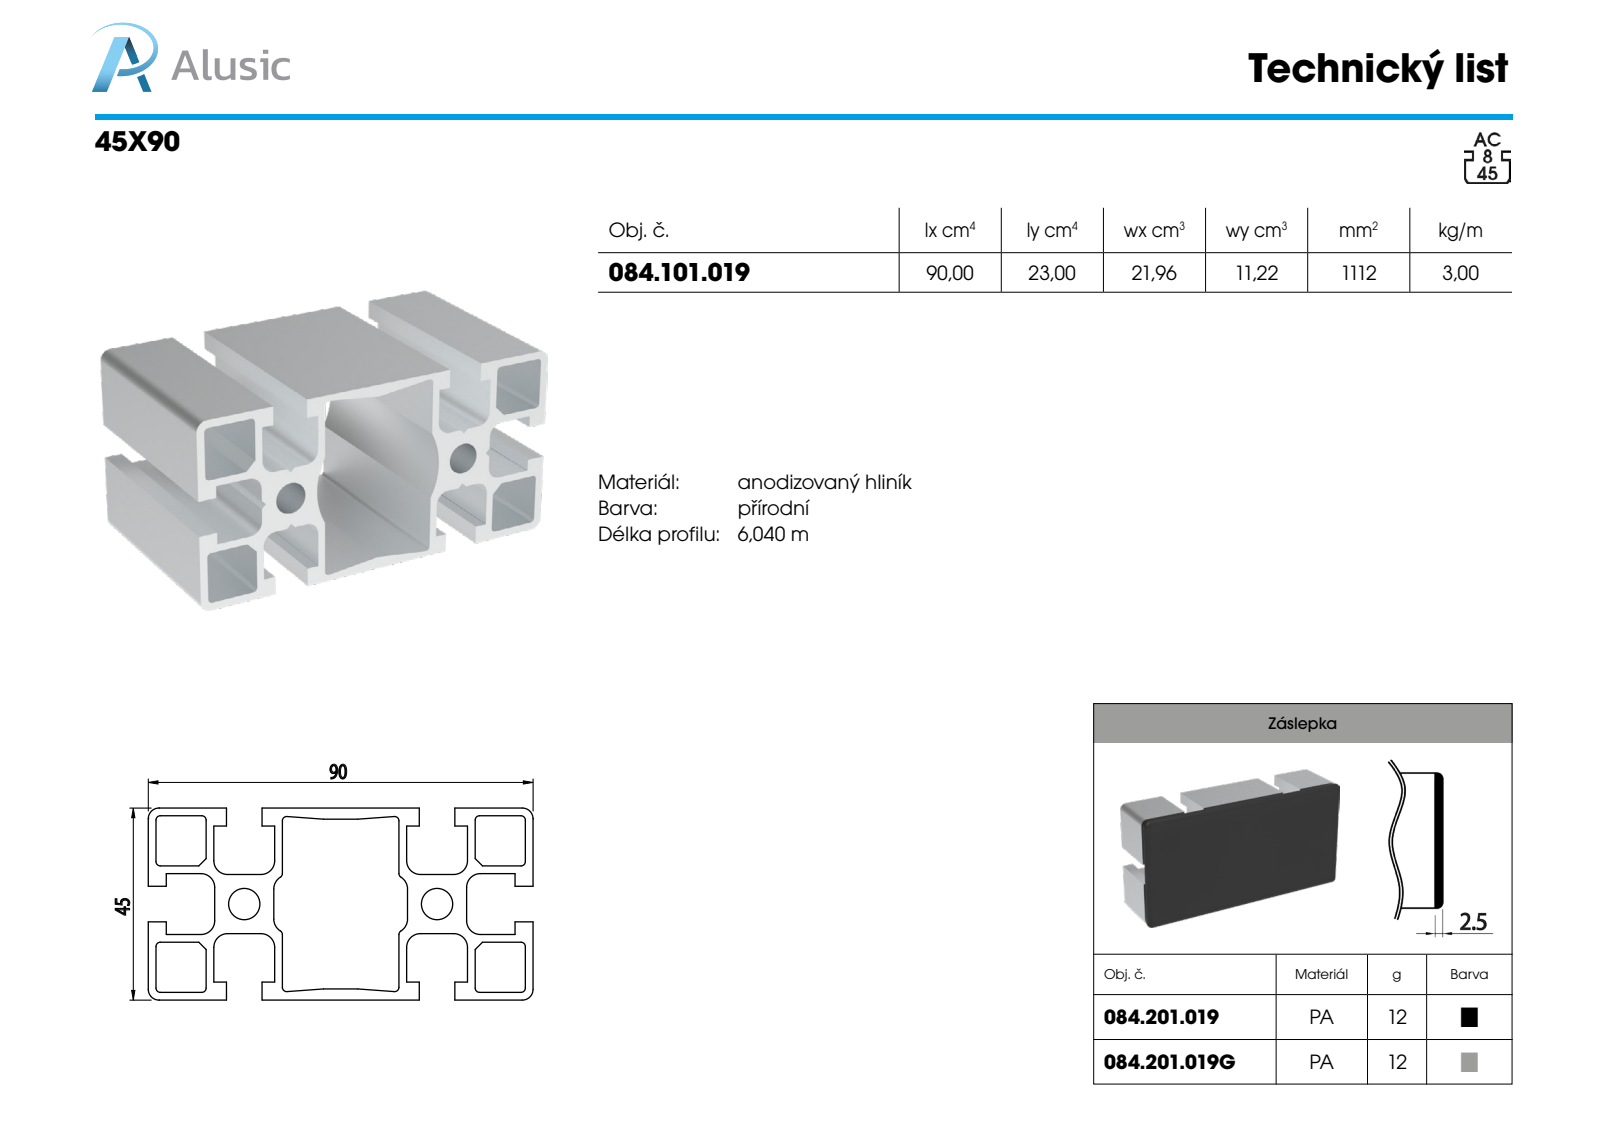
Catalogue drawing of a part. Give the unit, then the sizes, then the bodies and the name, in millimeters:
Units: millimetres
Overall size (bounding box): 90 × 45 × 12.2
Round holes (diameter × count): ⌀10 ×4
Round bosses / shafts (diameter × count): ⌀11.4 ×4
Partial cylindrical surfaces — rounded edges, fillets, slot ends (radius × count): R2 ×8, R3.65 ×2
Main face-to-face distances: 2.5, 21.9, 23.1, 1.2, 45, 3, 0.5, 66.9, 68.1, 7
Hole centre spacings: 29.5, 74.4, 80.04
Volume: 11 034 mm³ · Surface area: 11 250 mm²
Bodies: 1 solid, 122 faces (34 planar, 34 cylindrical, 54 other)
Part name (STEP PRODUCT): 084.201.019-2
STEP written by: SolidWorks 2011 (CONFIG_CONTROL_DESIGN)
